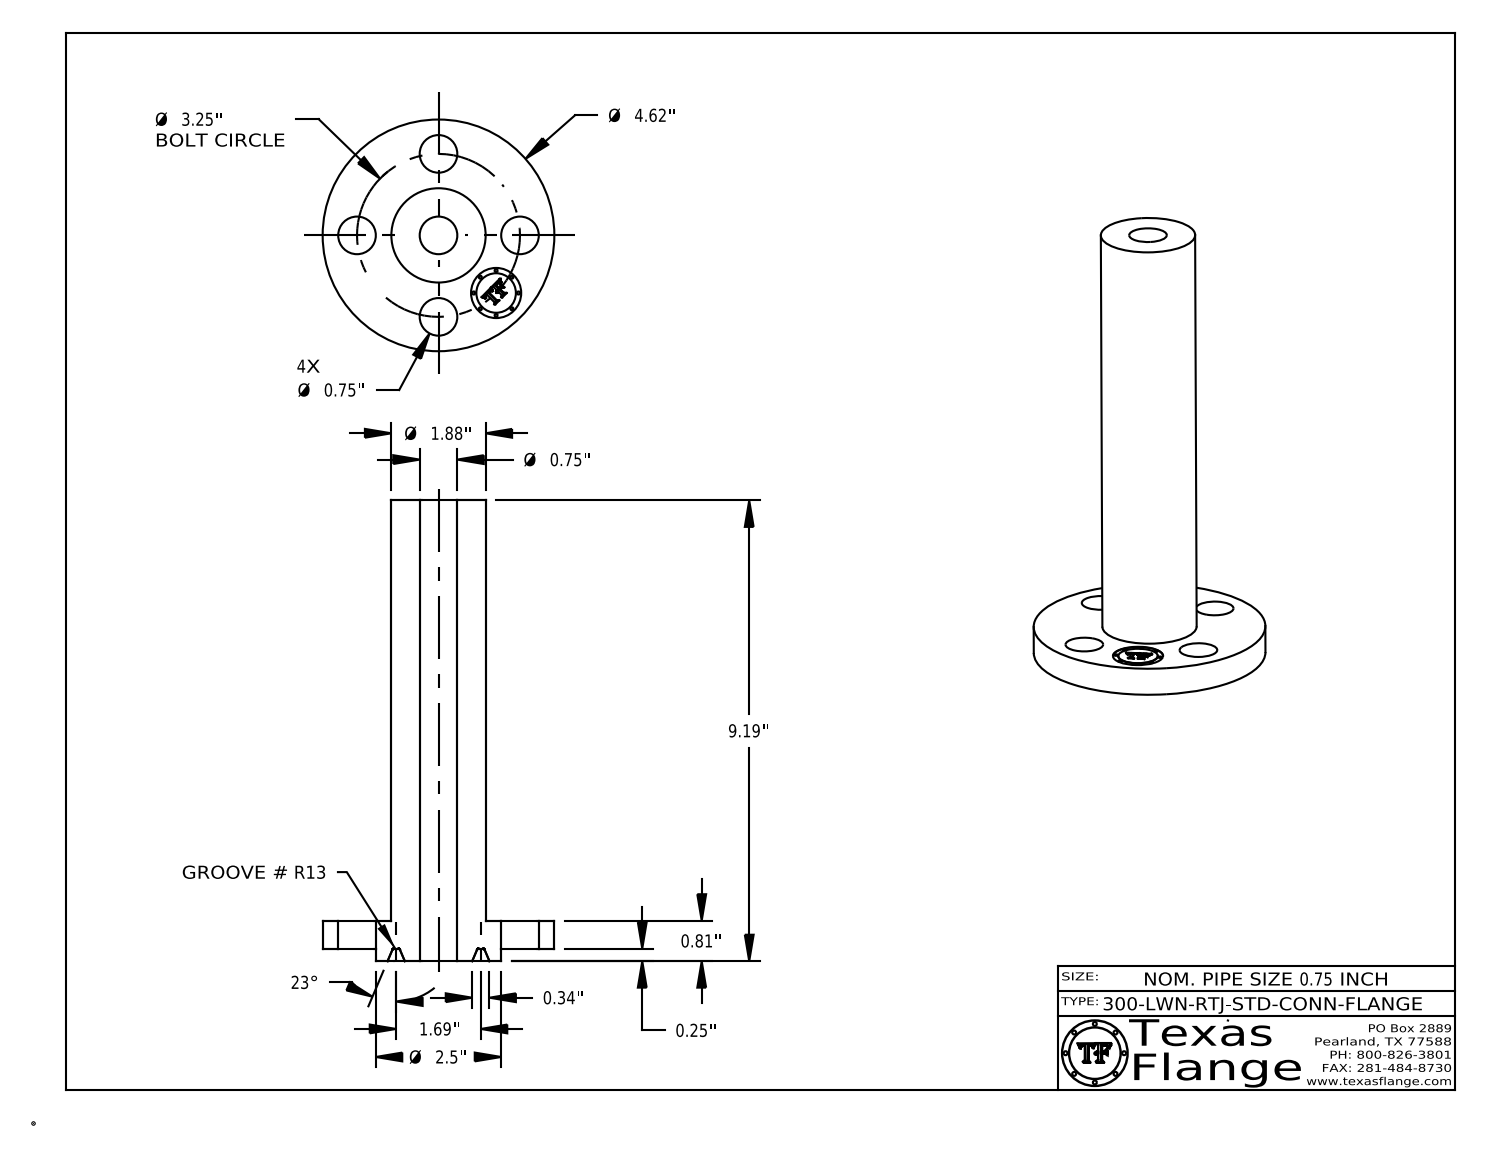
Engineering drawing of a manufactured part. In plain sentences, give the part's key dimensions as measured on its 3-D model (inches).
The part is named "0.75-300-LWN-RTJ-STD-CONN-FLANGE". Its 3-D file was written by "CATIA V5 STEP AP214 (AUTOMOTIVE_DESIGN)". It is 1 solid with 415 faces: 371 planar, 36 cylindrical and 8 other. Overall it measures 9.188 by 4.62 by 4.62 inches. Its volume is 28.47 cubic inches and its surface area 117.3 square inches. Round holes: 5 of diameter 0.75, 1 of diameter 1. Round bosses or shafts: 8 of diameter 0.061, 1 of diameter 4.62, 1 of diameter 2.5, 1 of diameter 1.88, 1 of diameter 0.788. The main face-to-face distances are 0.557, 0.25, 0.807, 9.187, 8.937, 8.38, 0.802, 0.552, 8.385, 0.298. The hole center spacings are 1.625, 2.298, 1.244, 3.003, 3.25.
